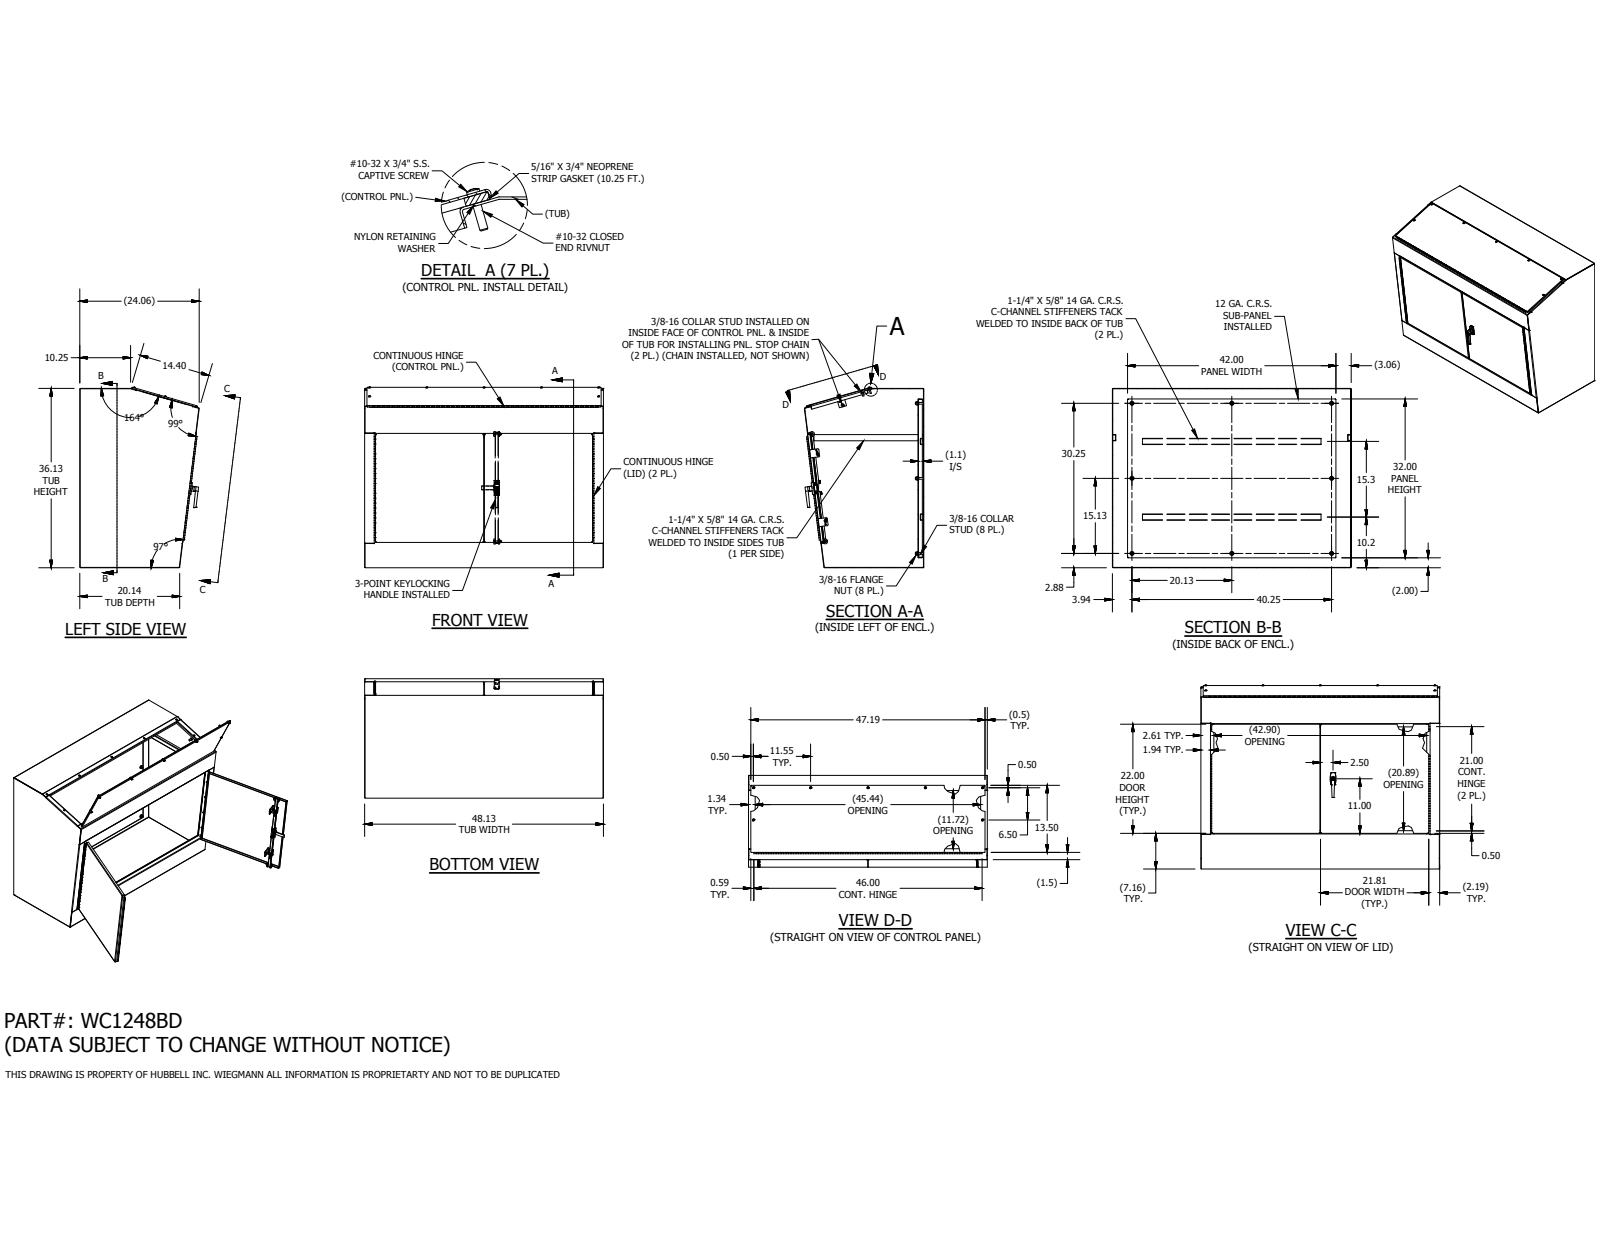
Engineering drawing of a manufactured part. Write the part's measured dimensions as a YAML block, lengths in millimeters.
part_name: "WC1248BD"
step_written_by: "SolidWorks 2019 (AUTOMOTIVE_DESIGN)"
units: millimeters
bodies: {solids: 93, faces: 3382, planar: 1934, cylindrical: 966, other: 482}
overall_size: [1222.4, 924, 611.1]
volume: 12390000
surface_area: 12490000
round_holes:
  - {diameter: 8, count: 19}
  - {diameter: 6.4, count: 9}
  - {diameter: 7, count: 8}
  - {diameter: 7.8, count: 8}
  - {diameter: 14.3, count: 8}
  - {diameter: 4, count: 7}
  - {diameter: 5, count: 7}
  - {diameter: 6.5, count: 7}
  - {diameter: 7.1, count: 7}
  - {diameter: 2.1, count: 5}
  - {diameter: 3.5, count: 5}
  - {diameter: 5.1, count: 4}
round_bosses_or_shafts:
  - {diameter: 8.4, count: 11}
  - {diameter: 15.9, count: 9}
  - {diameter: 11.5, count: 7}
  - {diameter: 10.3, count: 7}
  - {diameter: 6.3, count: 7}
  - {diameter: 4.2, count: 7}
  - {diameter: 4, count: 7}
  - {diameter: 6.4, count: 5}
partial_cylinders:
  - {radius: 3.5, count: 31}
  - {radius: 0.2, count: 25}
  - {radius: 1.6, count: 19}
  - {radius: 0.6, count: 16}
  - {radius: 1.6, count: 16}
  - {radius: 0.8, count: 14}
  - {radius: 0.8, count: 8}
  - {radius: 1.3, count: 8}
face_to_face_distances: [1.9, 1220.5, 2.4, 27.3, 25.4, 29.7, 27.8, 915.7, 1218.6, 1222.4]
hole_center_spacings: [293.3, 127, 586.6, 254, 29.3, 23, 29.4, 381]
